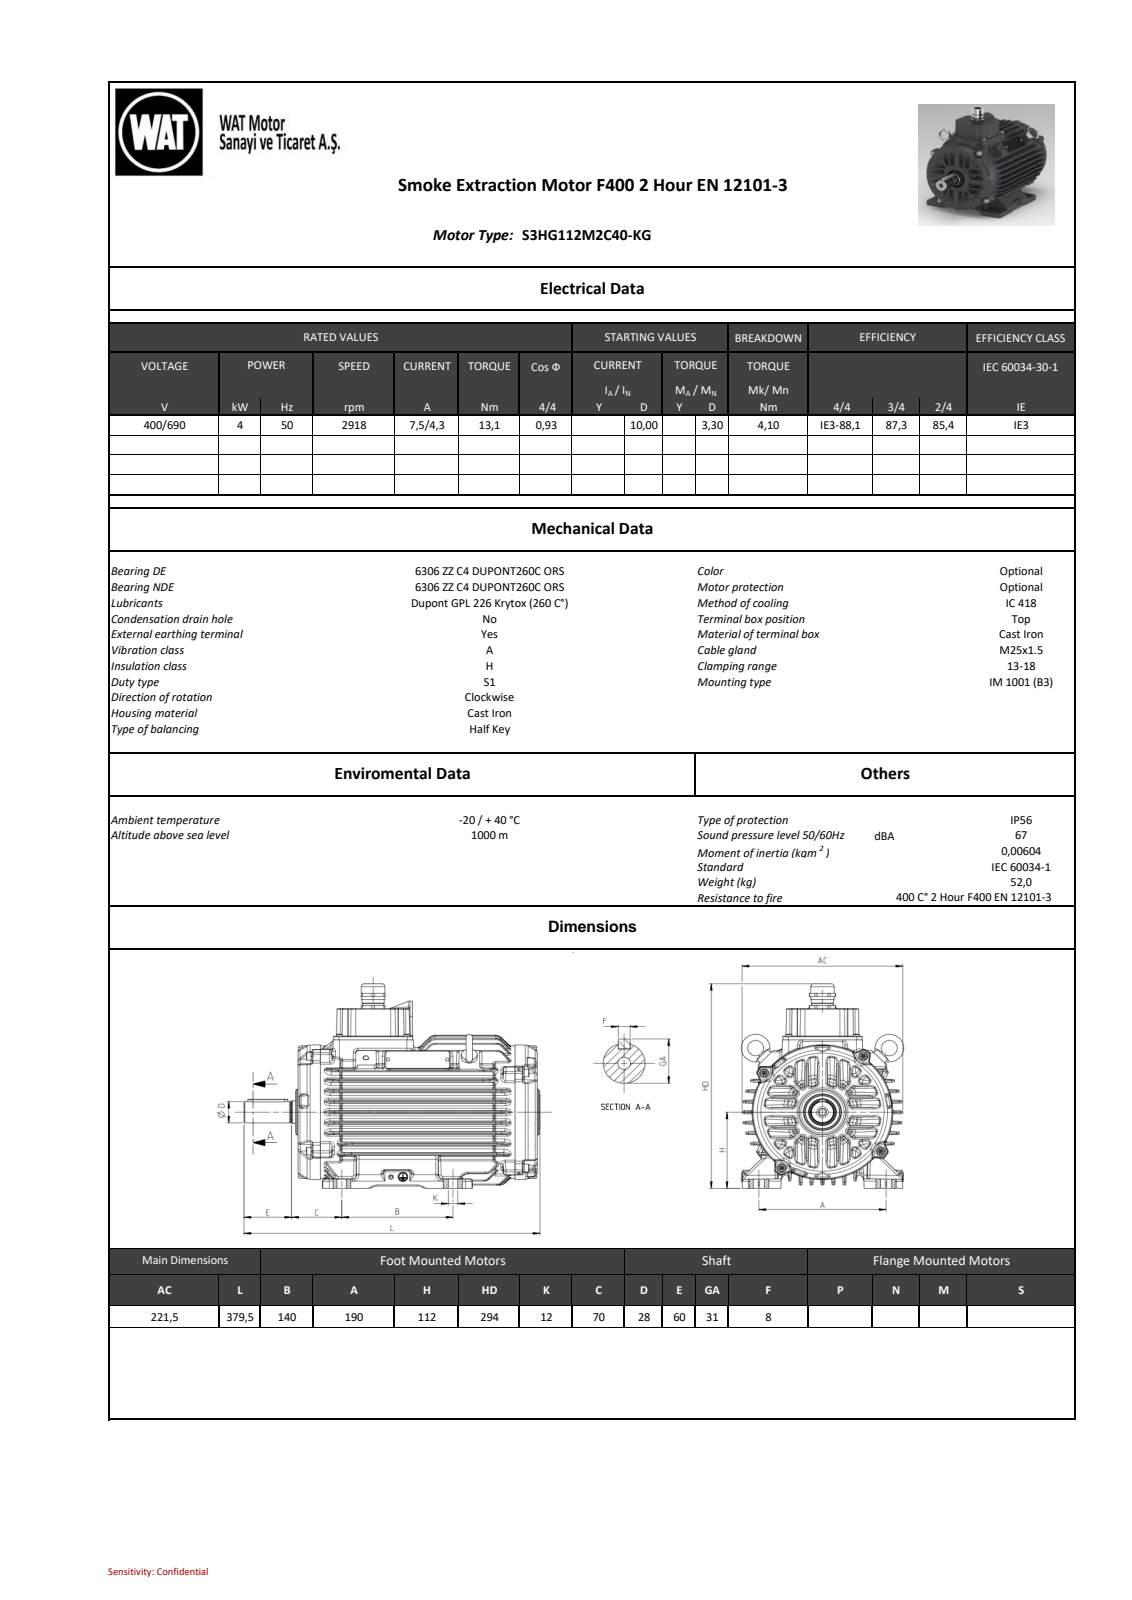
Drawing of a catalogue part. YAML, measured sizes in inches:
part_name: "26032C0836B7xil8"
step_written_by: "SIEMENS PLM Software NX 11.0 (AUTOMOTIVE_DESIGN)"
units: inches
bodies: {solids: 0, faces: 5915, planar: 837, cylindrical: 1354, other: 3724}
overall_size: [14.941, 11.563, 9.803]
round_holes:
  - {diameter: 0.197, count: 9}
  - {diameter: 0.13, count: 4}
  - {diameter: 0.098, count: 2}
  - {diameter: 0.268, count: 2}
  - {diameter: 0.335, count: 1}
  - {diameter: 0.413, count: 1}
  - {diameter: 0.709, count: 1}
  - {diameter: 1.299, count: 1}
  - {diameter: 1.693, count: 1}
round_bosses_or_shafts:
  - {diameter: 0.492, count: 8}
  - {diameter: 0.394, count: 8}
  - {diameter: 0.315, count: 4}
  - {diameter: 0.787, count: 2}
  - {diameter: 7.559, count: 1}
  - {diameter: 1.85, count: 1}
  - {diameter: 1.181, count: 1}
  - {diameter: 1.165, count: 1}
partial_cylinders:
  - {radius: 0.157, count: 285}
  - {radius: 0.118, count: 197}
  - {radius: 0.059, count: 98}
  - {radius: 0.197, count: 57}
  - {radius: 0.079, count: 53}
  - {radius: 0.01, count: 49}
  - {radius: 0.071, count: 48}
  - {radius: 0.039, count: 36}
face_to_face_distances: [0.516, 1.573, 1.035, 0.519, 3.565, 1.557, 1.041, 0.522, 3.046, 2.53]
hole_center_spacings: [3.819, 5.401, 1.326, 4.381, 6.257, 7.522, 7.638, 1.083]
